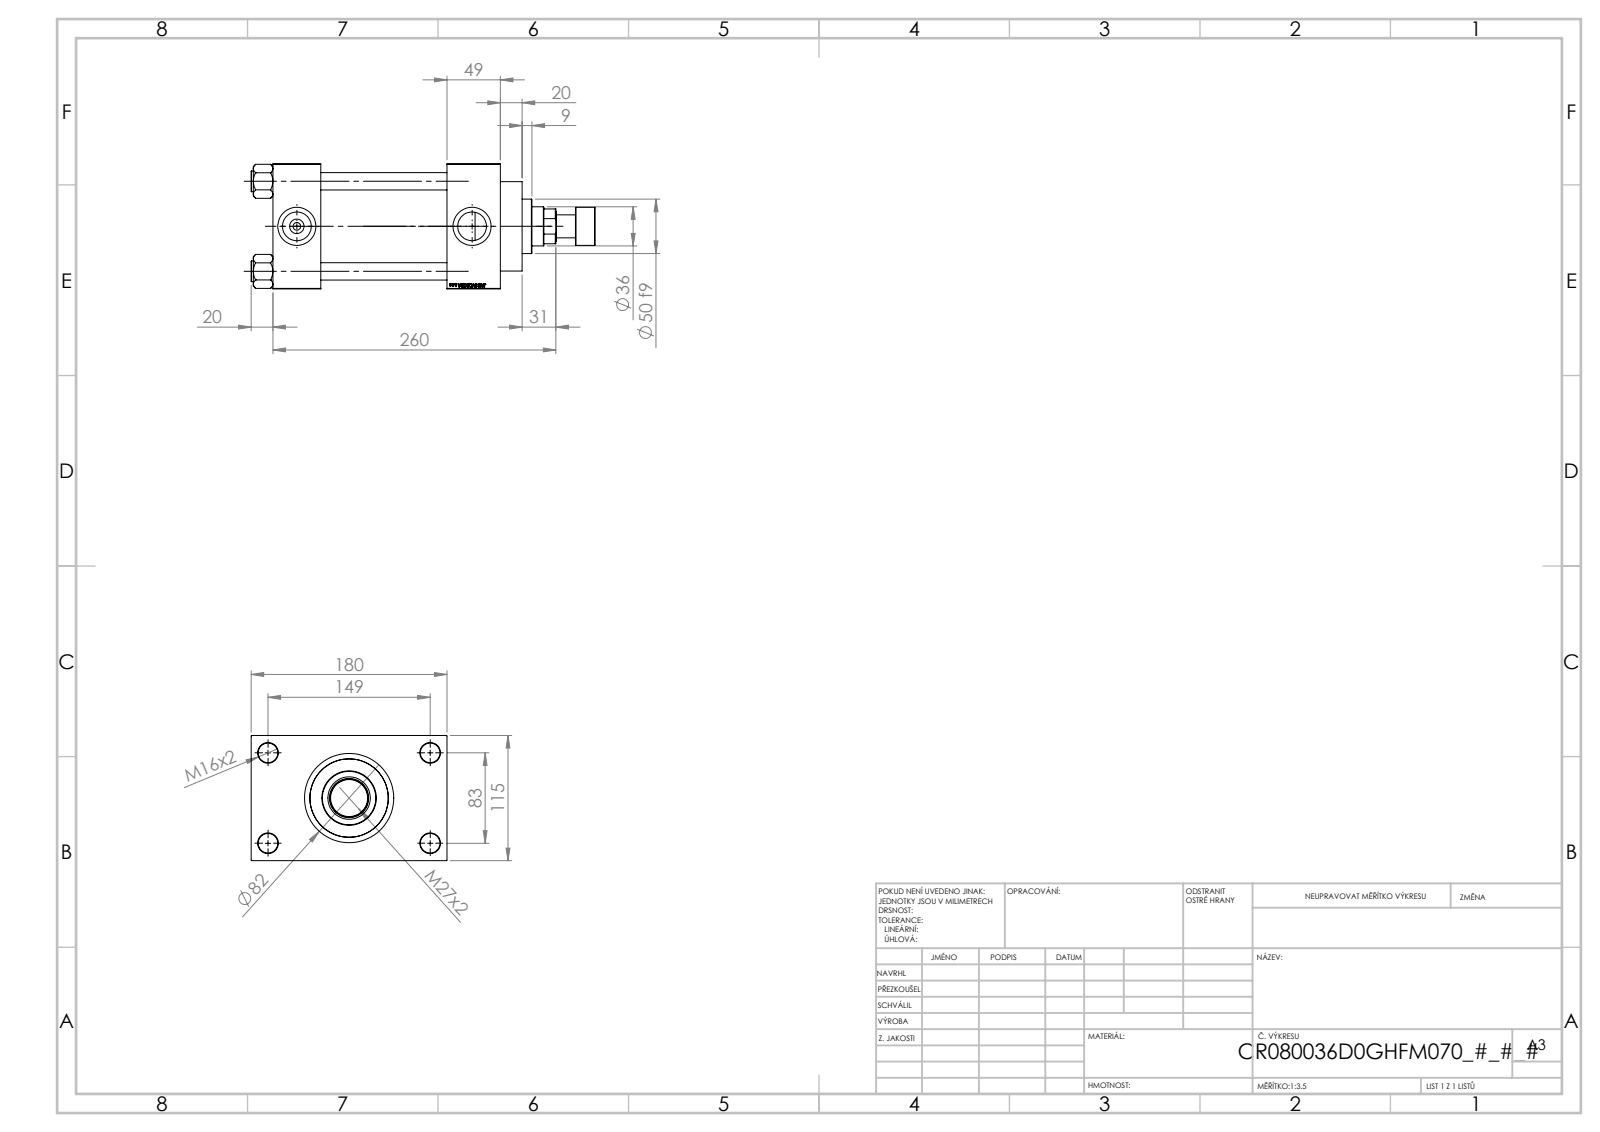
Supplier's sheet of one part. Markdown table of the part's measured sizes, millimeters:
| quantity | value |
| --- | --- |
| part name | V215CR_VCP_D; V215CR_ROD_END_F; V215CR_D_Body; NUT_M5_D (+2 more) |
| STEP written by | SolidWorks 2019 (CONFIG_CONTROL_DESIGN) |
| units | millimeters |
| bodies | 12 solids, 1165 faces (549 planar, 92 cylindrical, 524 other) |
| overall size | 316 × 180 × 115 |
| volume | 2 133 000 mm³ |
| surface area | 343 945 mm² |
| round holes (diameter × count) | 16 × 4, 18 × 4, 7 × 2, 26.44 × 2, 35 × 2, 25.5 × 1, 36 × 1, 39 × 1, 61 × 1, 72 × 1, 80 × 1 |
| round bosses / shafts (diameter × count) | 19 × 4, 86 × 1, 82 × 1, 50 × 1, 35 × 1, 21 × 1 |
| main face-to-face distances | 115, 116, 49, 165, 44, 160, 209, 32.5, 147.5, 180 |
| hole center spacings | 33.15, 58.48, 82.7, 85.28, 89.24, 115.85, 142.43, 83 |
